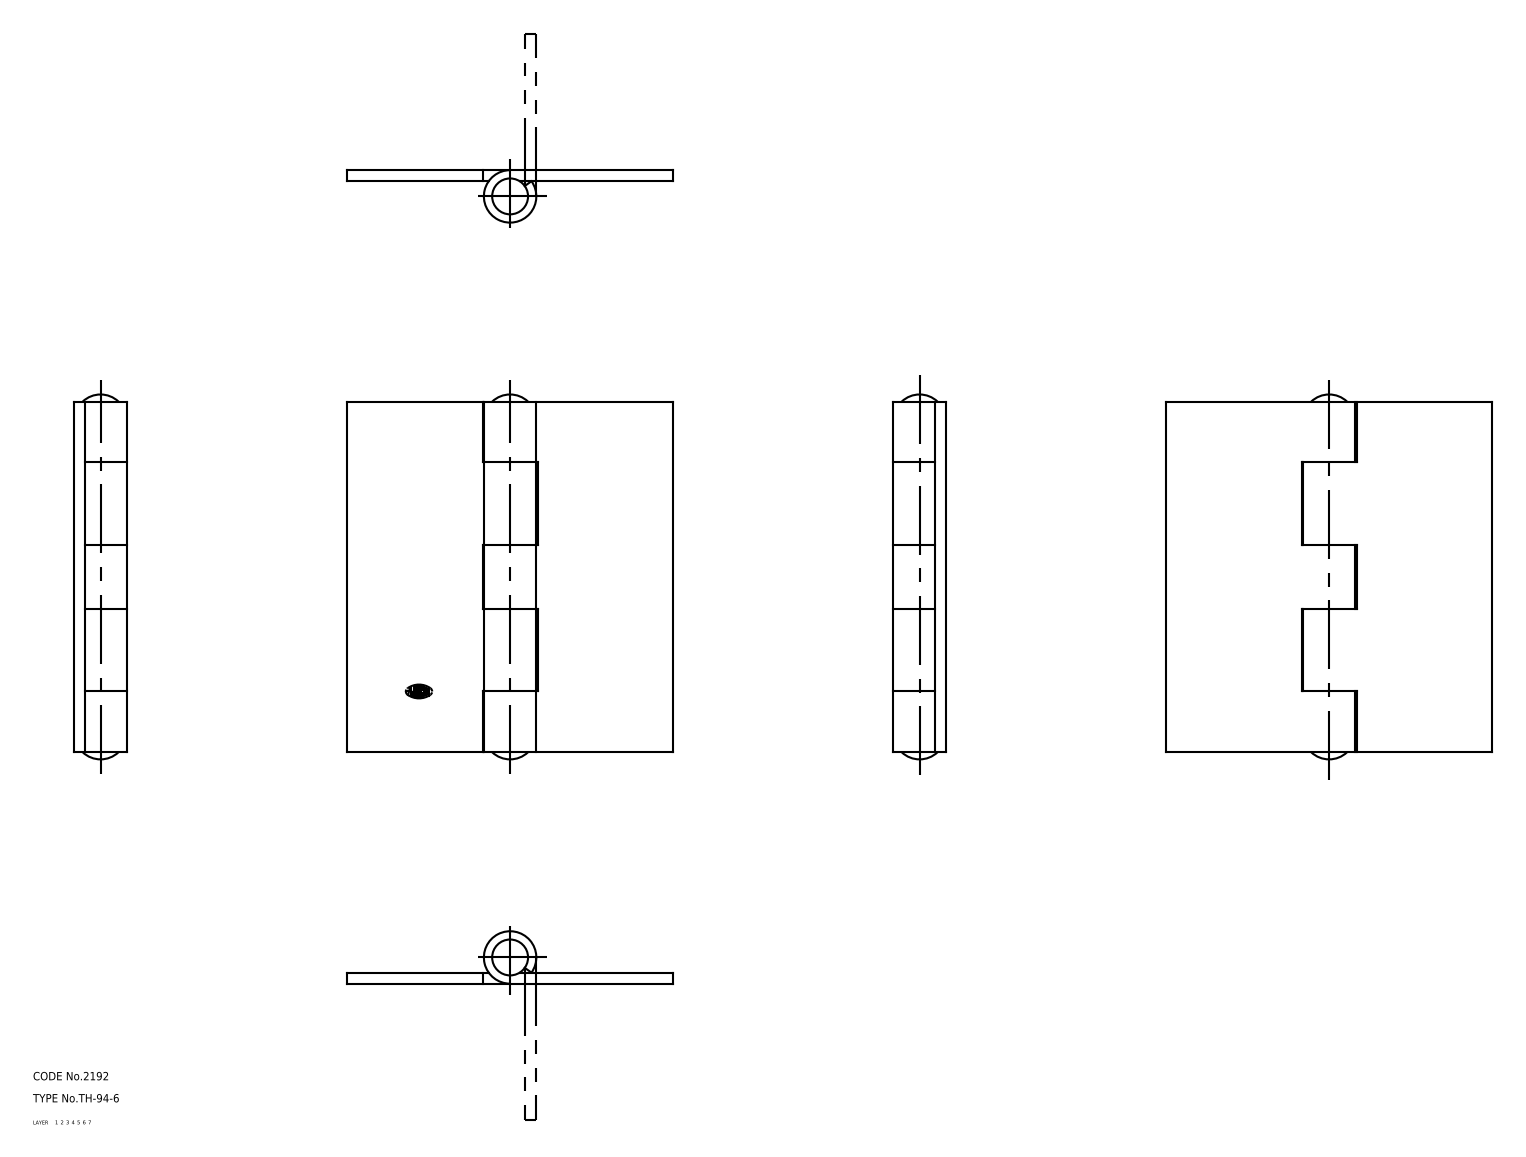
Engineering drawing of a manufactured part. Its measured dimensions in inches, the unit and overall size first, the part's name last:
Units: inches
Overall size (bounding box): 5.205 × 4.646 × 0.748
Volume: 5.346 in³ · Surface area: 73.1 in²
Bodies: 3 solids, 44 faces (0 planar, 0 cylindrical, 44 other)
Part name (STEP PRODUCT): hinge piece_B; hinge piece_A; shaft; TH_94_6_19123_36
STEP written by: CADfix (AUTOMOTIVE_DESIGN)
